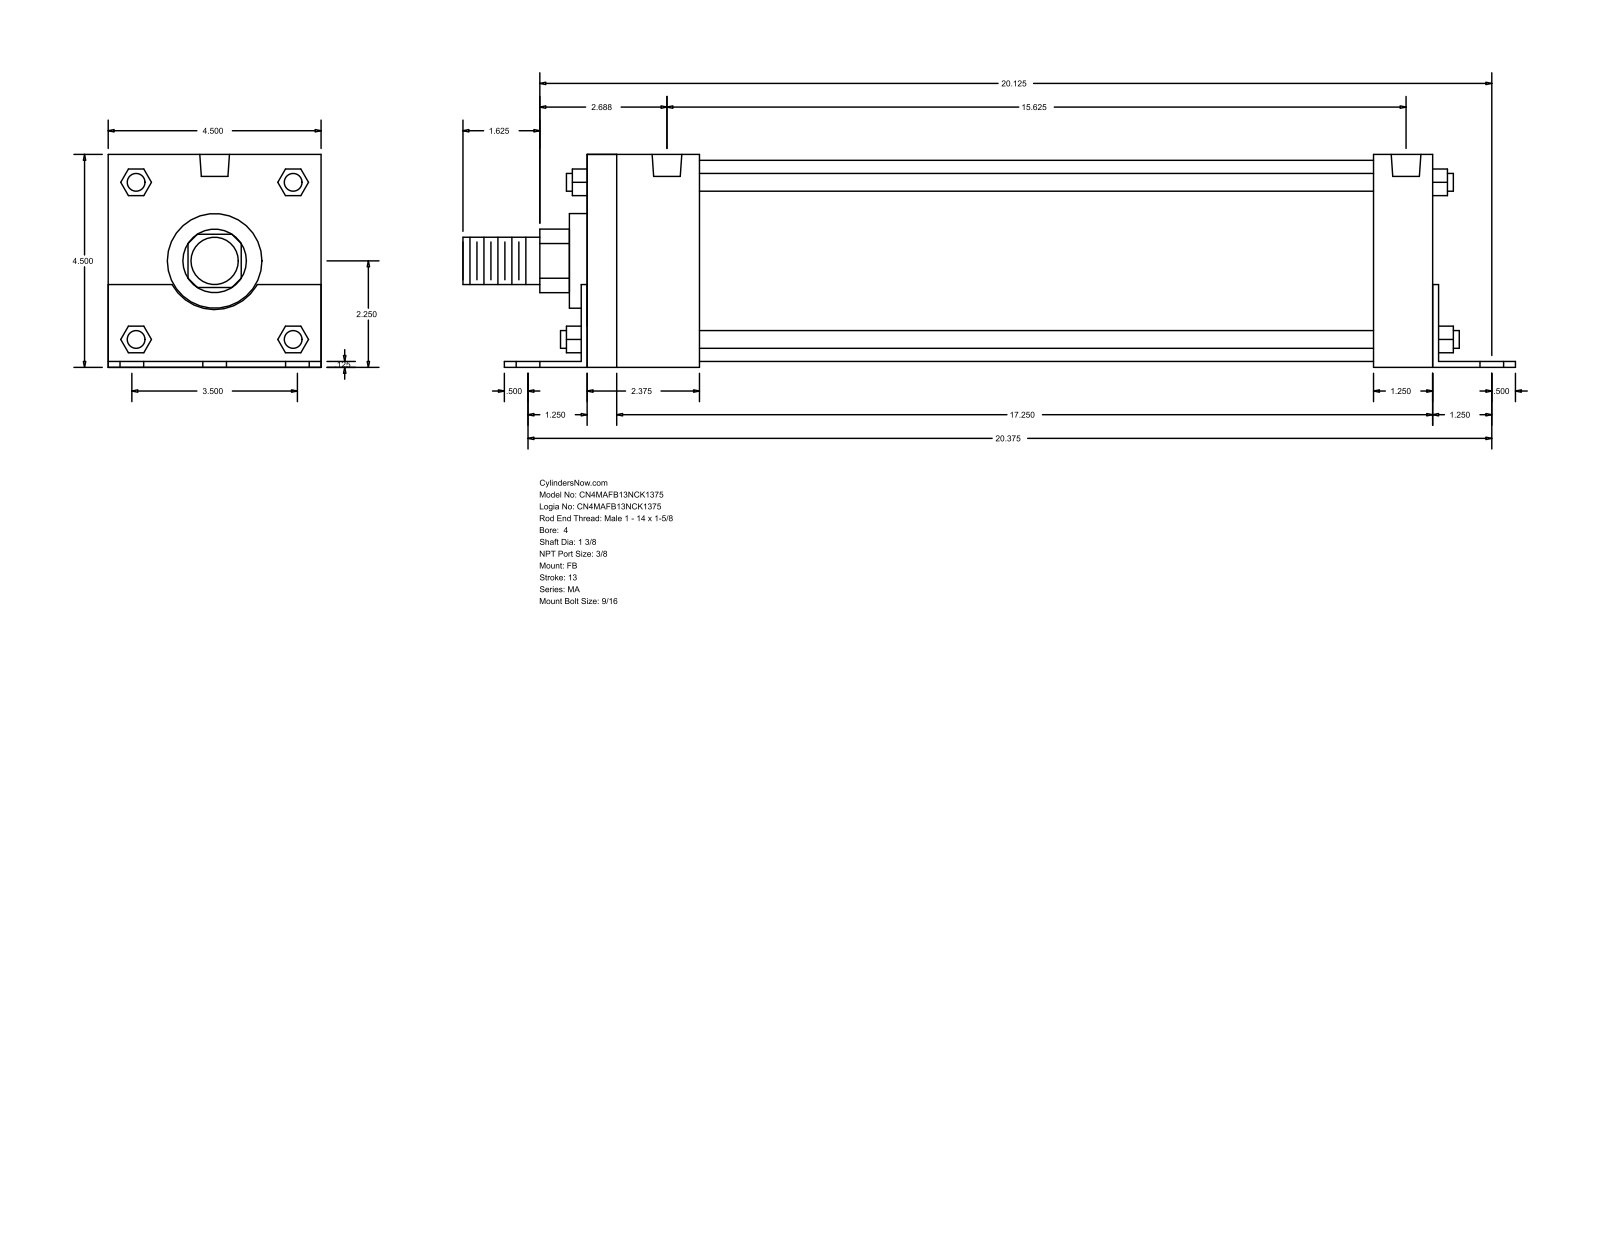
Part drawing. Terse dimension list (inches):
name: MA_FB__0400_1.375
written by: GSSL Pune (CONFIG_CONTROL_DESIGN)
unit: in
bodies: 0 solids, 140 faces (105 planar, 35 cylindrical, 0 other)
size: 22.25 × 4.502 × 4.5
holes: 6× ⌀0.563, 4× ⌀0.437, 2× ⌀0.627
bosses: 4× ⌀0.375, 1× ⌀4.25, 1× ⌀2, 1× ⌀1.375, 1× ⌀1
rounds: 1× R0.672, 1× R1.03
face distances: 4.5, 0.125, 4.502, 0.123, 4.377, 18, 17.875, 18.125, 1.25, 16.75
hole spacings: 1.75, 20.45, 20.375, 2.52, 2.657, 3.419, 3.5, 3.582
